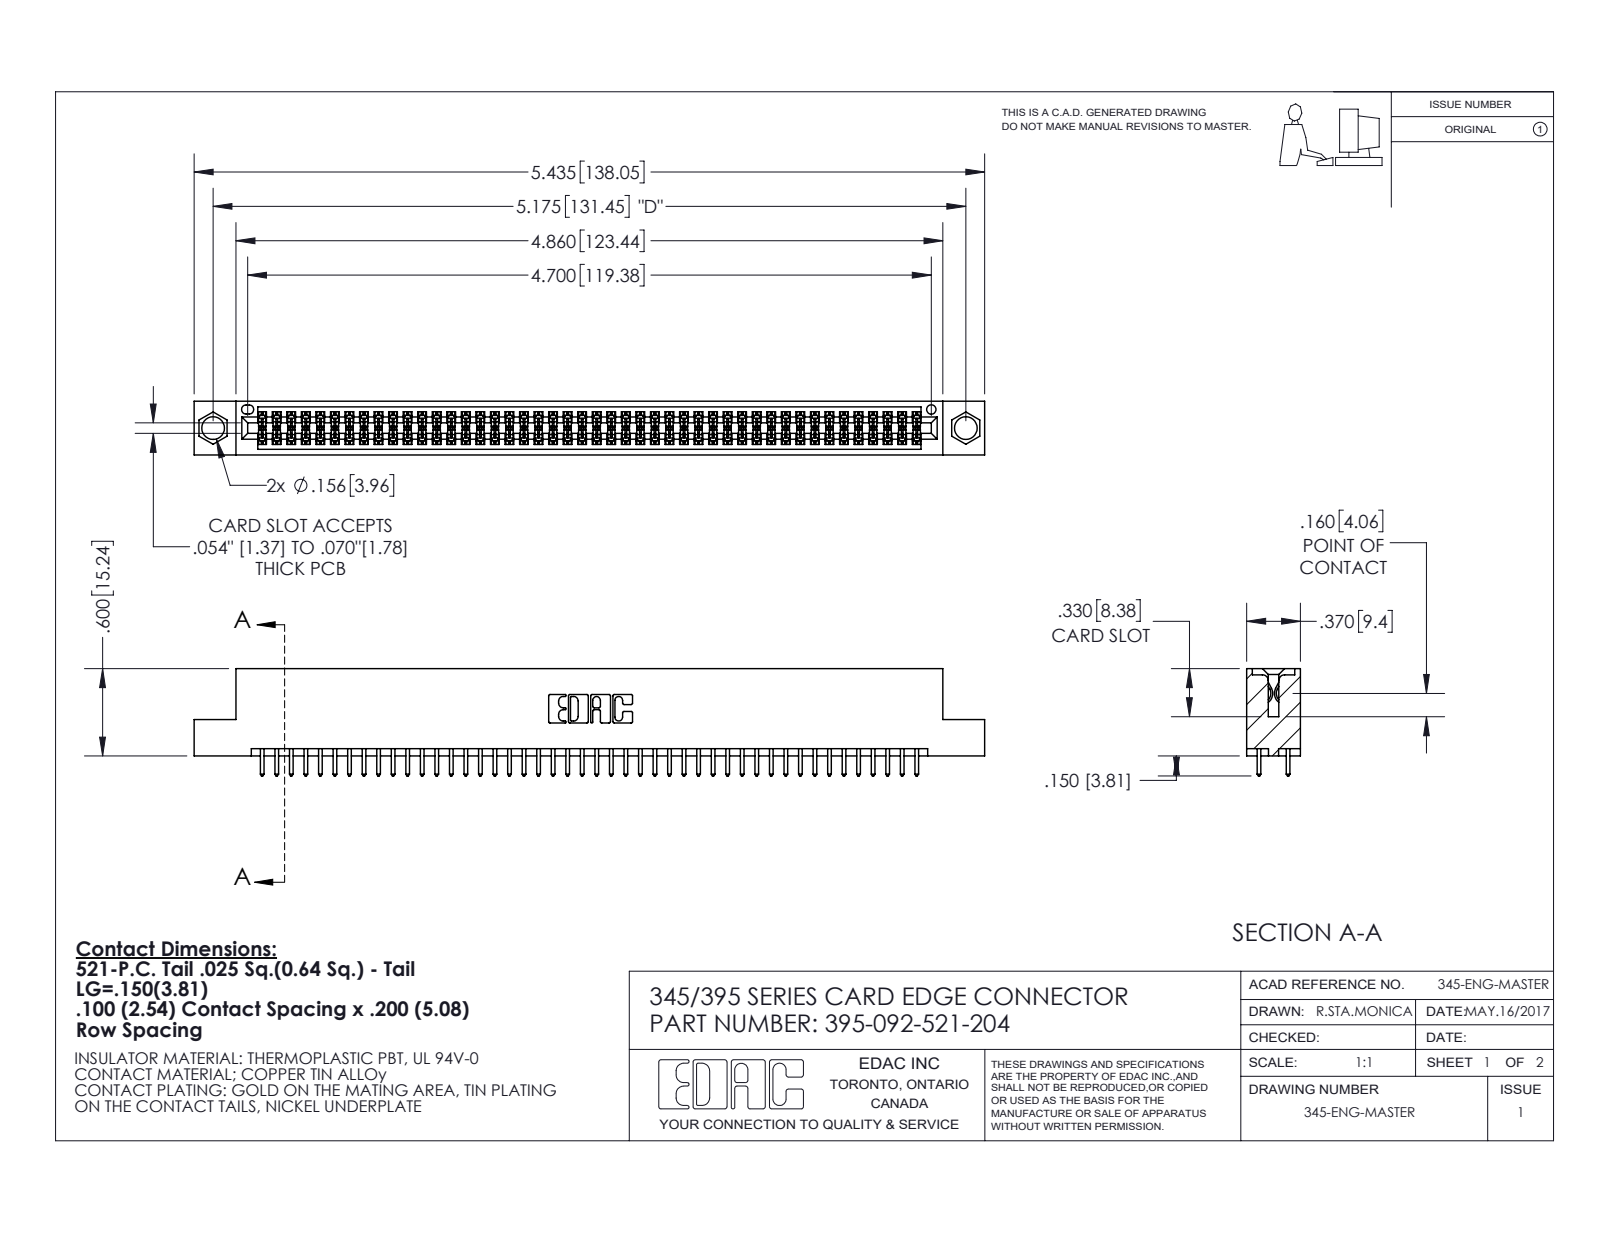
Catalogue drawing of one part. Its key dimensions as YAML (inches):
part_name: "345 Part_Flush Mounting Lugs - 0.156 Dia-TI; 395-092-521-204; 345-292-001_345-293-121"
step_written_by: "SolidWorks 2020 (CONFIG_CONTROL_DESIGN)"
units: inches
bodies: {solids: 93, faces: 4740, planar: 3130, cylindrical: 1610, other: 0}
overall_size: [5.435, 0.737, 0.37]
volume: 0.812
surface_area: 29.99
round_holes:
  - {diameter: 0.156, count: 2}
  - {diameter: 0.064, count: 1}
partial_cylinders:
  - {radius: 0.006, count: 184}
  - {radius: 0.01, count: 92}
  - {radius: 0.01, count: 22}
  - {radius: 0.007, count: 6}
  - {radius: 0.031, count: 6}
  - {radius: 0.026, count: 3}
  - {radius: 0.014, count: 2}
  - {radius: 0.019, count: 2}
face_to_face_distances: [0.072, 0.298, 0.2, 0.37, 0.098, 0.272, 0.025, 0.225, 0.175, 0.149]
hole_center_spacings: [0.27, 4.939, 5.175]
